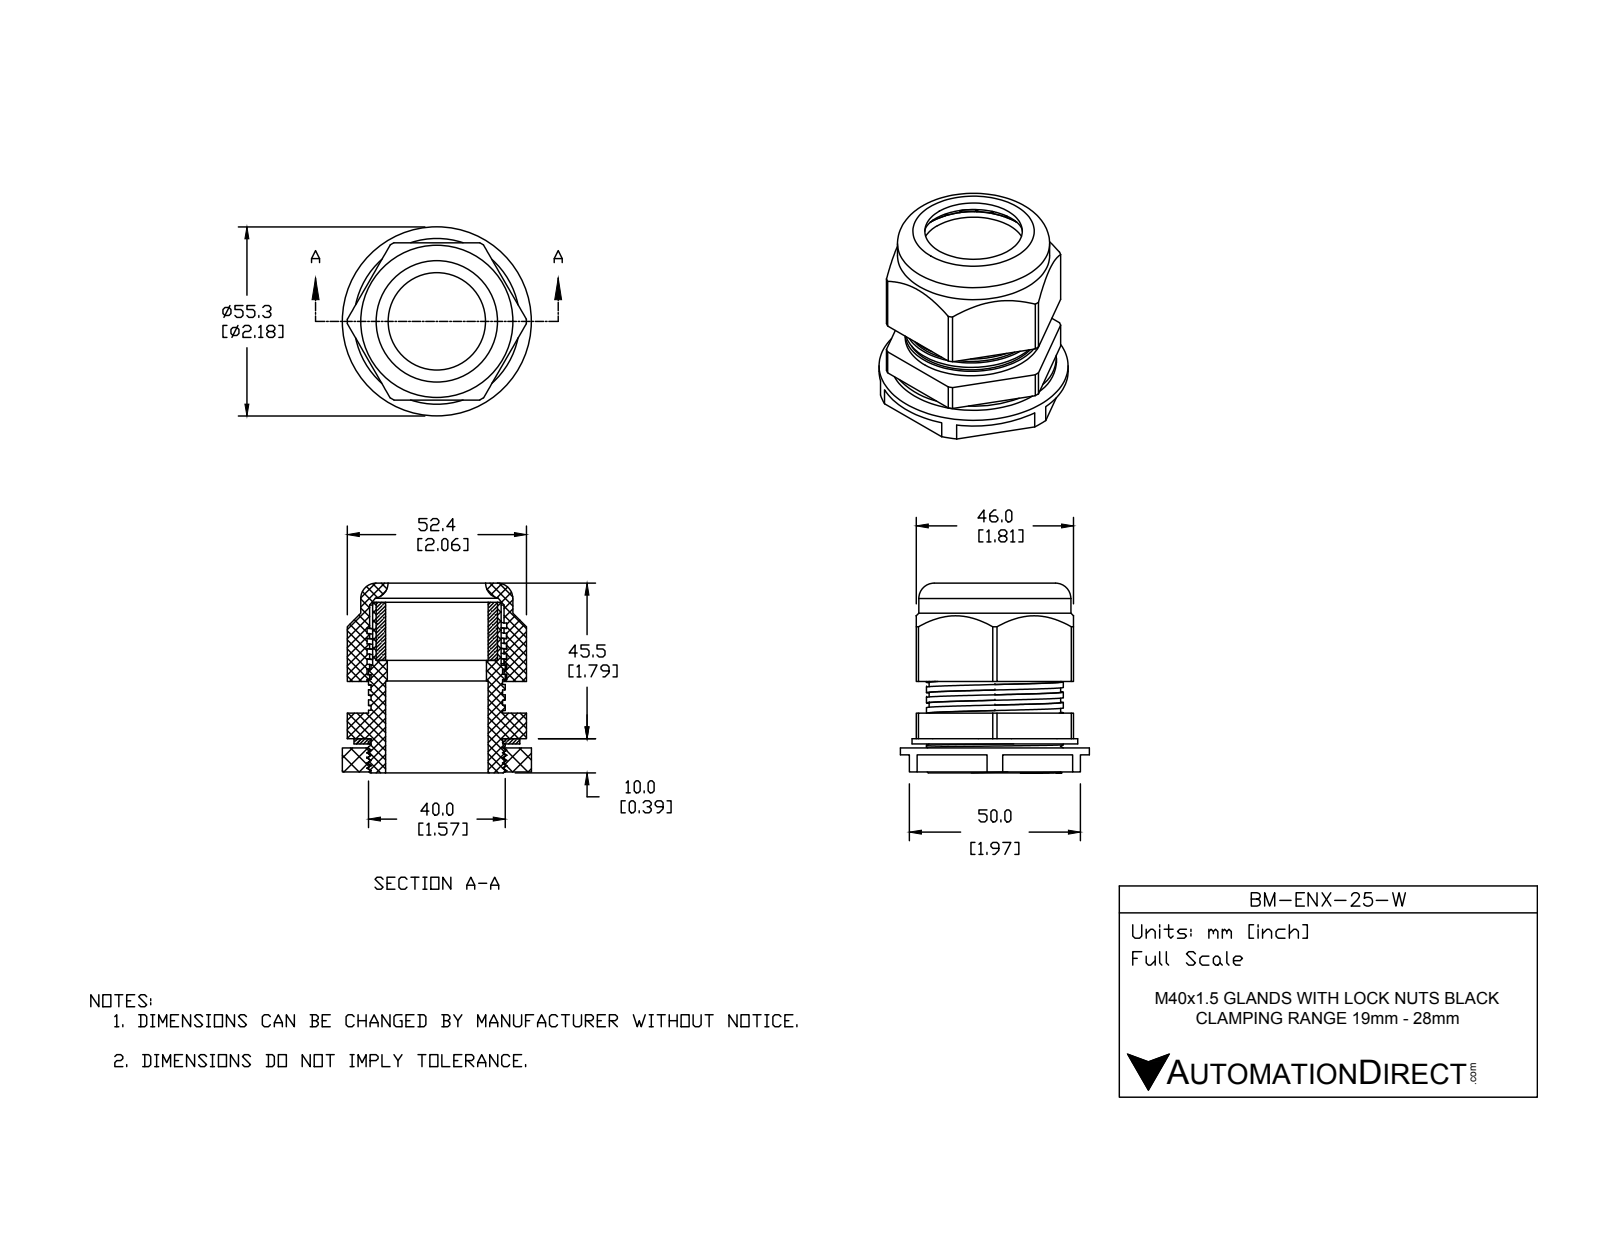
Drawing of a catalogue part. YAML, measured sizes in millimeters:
part_name: "BM-ENX-25-W"
step_written_by: "SolidWorks 2015 (CONFIG_CONTROL_DESIGN)"
units: millimeters
bodies: {solids: 5, faces: 243, planar: 140, cylindrical: 82, other: 21}
overall_size: [55.5, 55.3, 55.3]
volume: 51903
surface_area: 36921
round_holes:
  - {diameter: 29, count: 1}
  - {diameter: 30, count: 1}
  - {diameter: 35.5, count: 1}
  - {diameter: 38.5, count: 1}
  - {diameter: 39.33, count: 1}
round_bosses_or_shafts:
  - {diameter: 55.3, count: 1}
  - {diameter: 48.5, count: 1}
  - {diameter: 44.5, count: 1}
  - {diameter: 40, count: 1}
  - {diameter: 37.6, count: 1}
partial_cylinders:
  - {radius: 26.2, count: 1}
face_to_face_distances: [46, 2.5, 7.5, 10, 48, 17, 32.4, 2, 7, 9.5]
